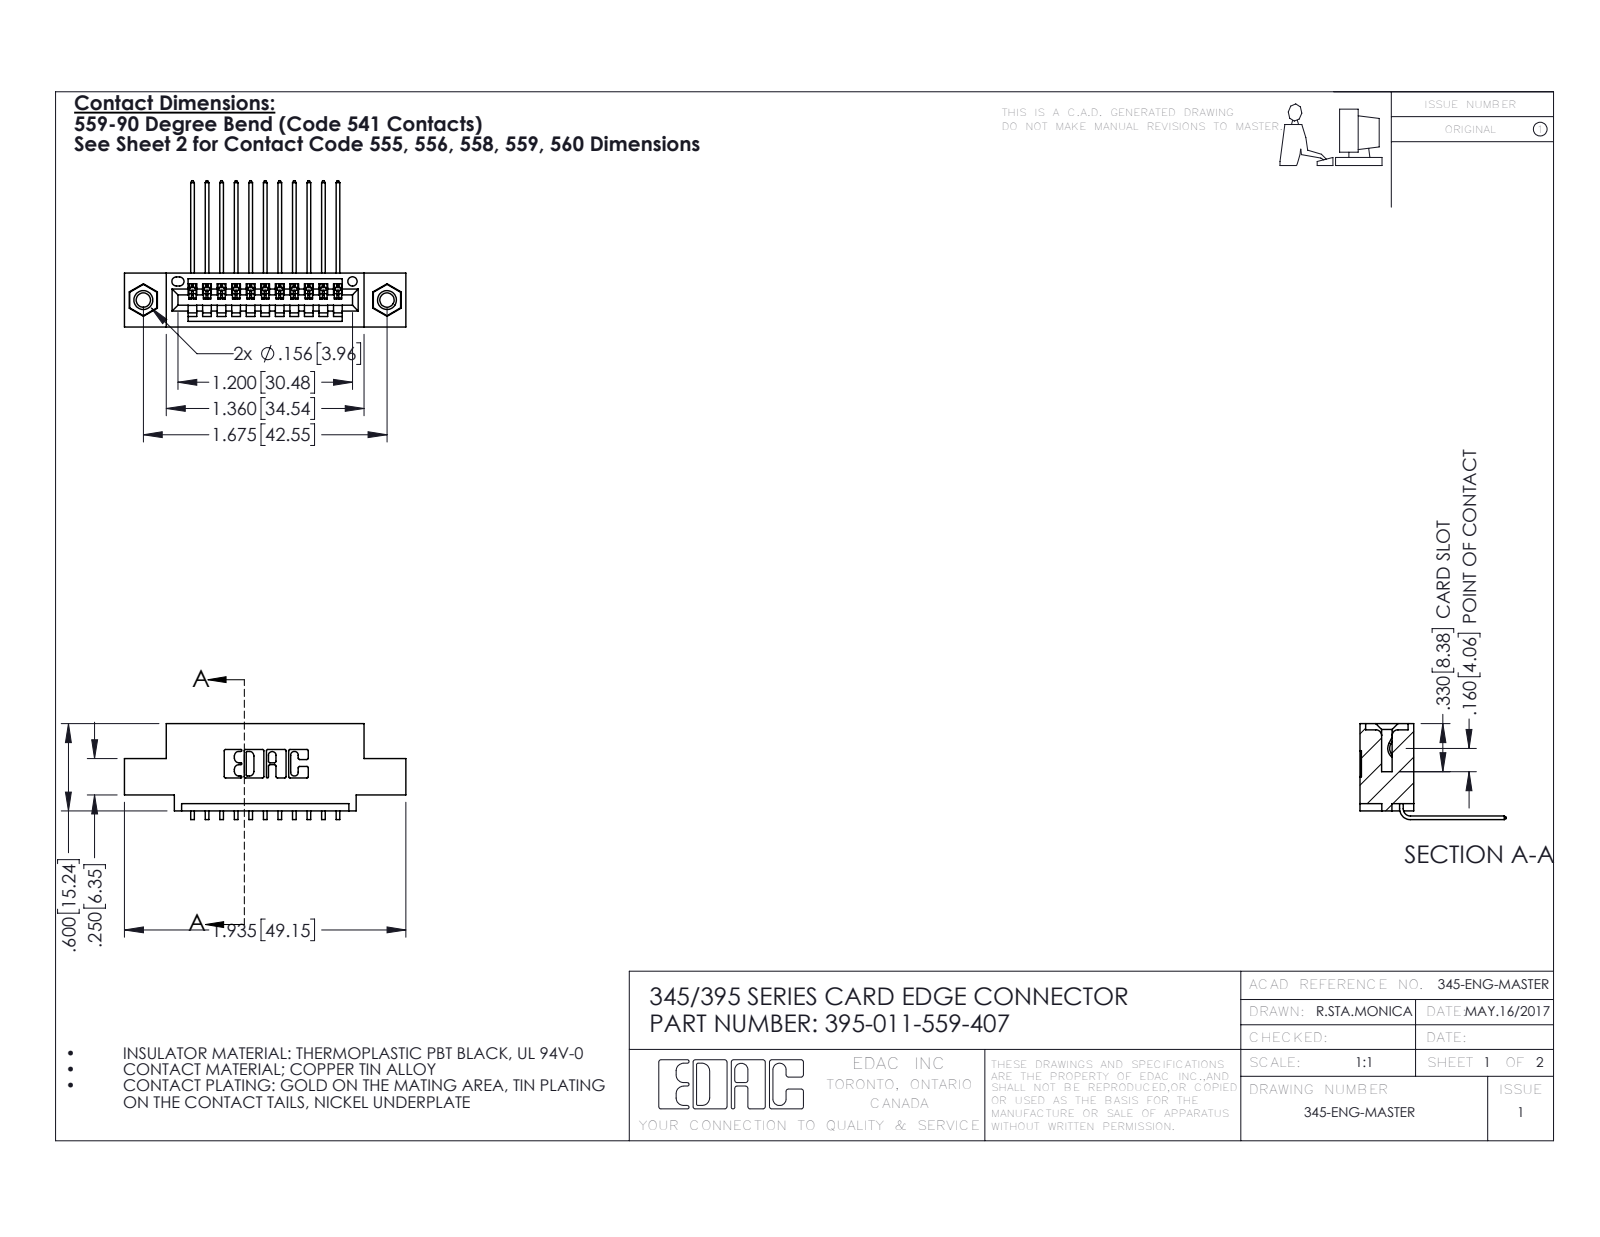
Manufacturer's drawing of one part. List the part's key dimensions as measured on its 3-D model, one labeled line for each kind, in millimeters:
Part name (STEP PRODUCT): 395-011-559-407; 345-250-001_345-250-005-103; 345-292-001_558 559 Tail - 1; 345 Part_0.110 Offset - 0.156 Dia-TI
STEP written by: SolidWorks 2016 (CONFIG_CONTROL_DESIGN)
Units: millimetres
Bodies: 14 solids, 850 faces (578 planar, 256 cylindrical, 16 other)
Overall size (bounding box): 49.1 × 25.5 × 16.7
Volume: 4 360 mm³ · Surface area: 5 708 mm²
Round holes (diameter × count): ⌀2.5 ×2, ⌀3.2 ×2, ⌀4 ×2, ⌀1.6 ×1
Round bosses / shafts (diameter × count): ⌀3.9 ×2
Partial cylindrical surfaces — rounded edges, fillets, slot ends (radius × count): R0.2 ×22, R0.3 ×22, R0.2 ×6, R0.8 ×6, R0.7 ×3, R0.8 ×2, R1 ×2, R0.4 ×1
Main face-to-face distances: 5.1, 1.8, 7.6, 9.4, 2.5, 6.9, 0.6, 2.5, 15.2, 1.5
Hole centre spacings: 6.9, 36.7, 42.5
